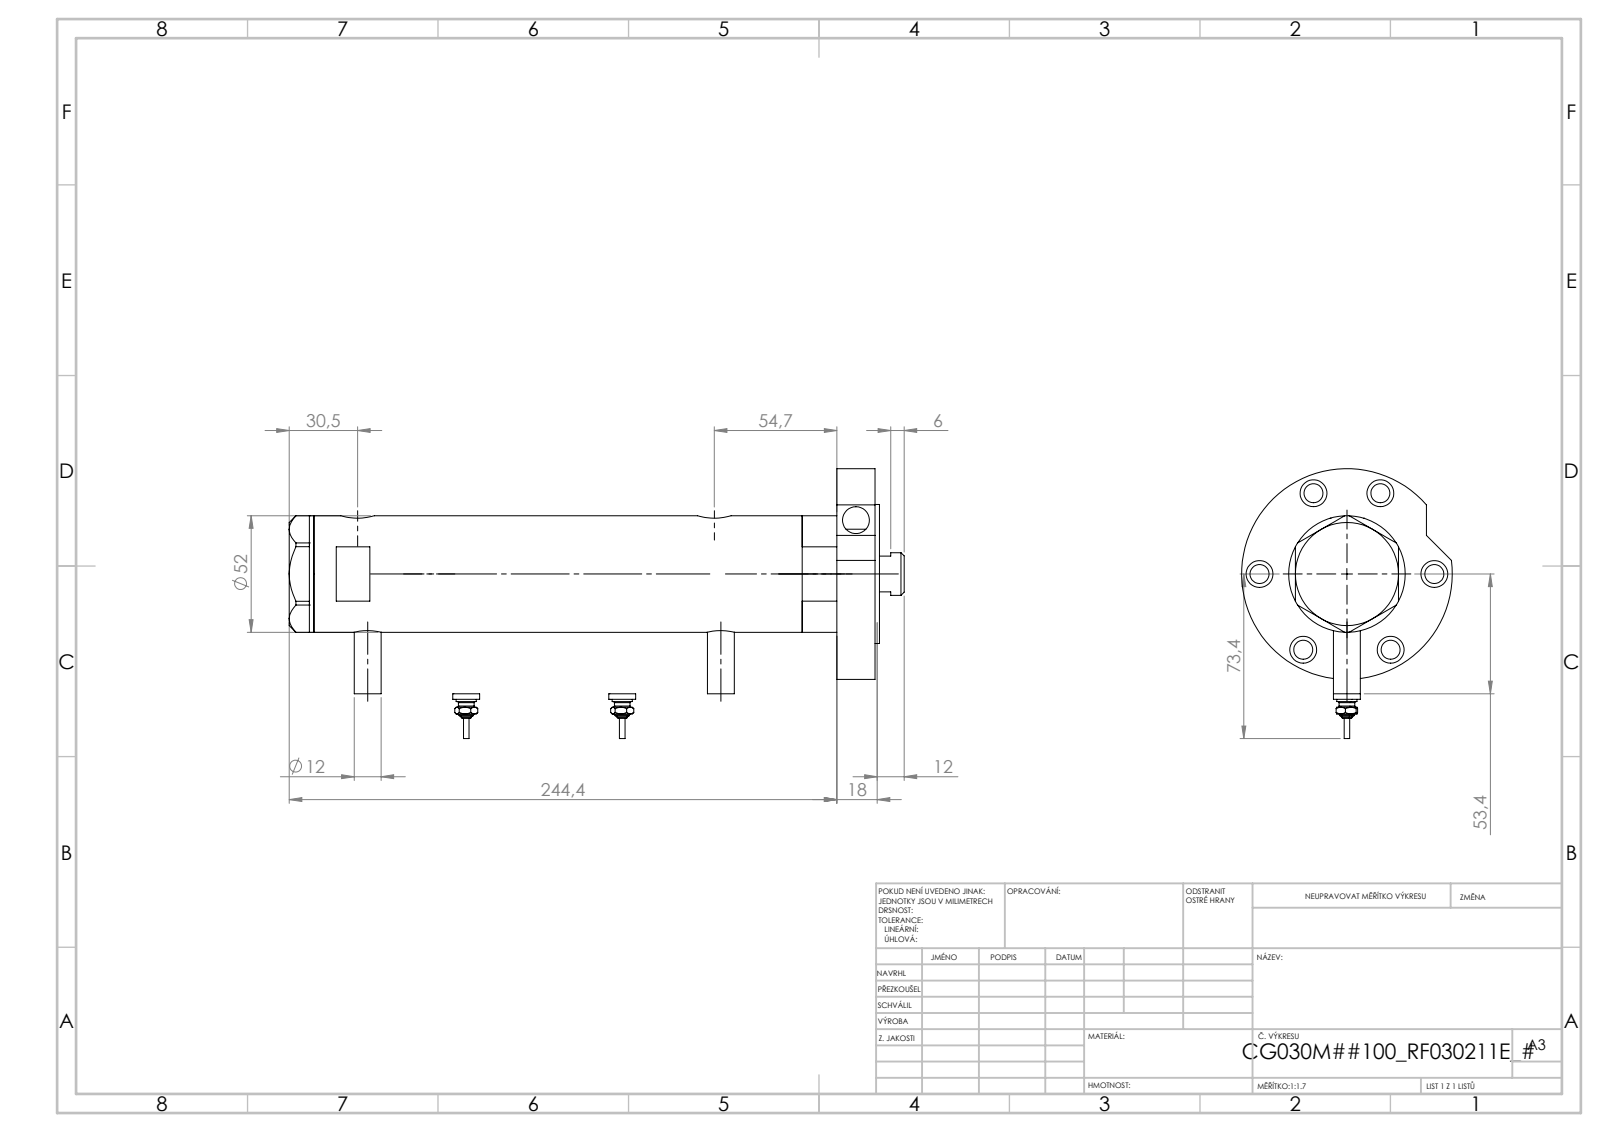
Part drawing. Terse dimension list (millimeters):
name: V270CG_FRONT; V270CG_VC; V270CG_RF211E; V270CG_BACK (+2 more)
written by: SolidWorks 2019 (CONFIG_CONTROL_DESIGN)
unit: mm
bodies: 7 solids, 290 faces (106 planar, 110 cylindrical, 74 other)
size: 249.02 × 105.3 × 94
volume: 525 288 mm³; area: 122 862 mm²
holes: 7× ⌀12, 6× ⌀8.5, 2× ⌀5, 2× ⌀9.73, 2× ⌀12.5, 2× ⌀15, 1× ⌀6.5, 1× ⌀20, 1× ⌀21.5, 1× ⌀30, 1× ⌀33, 1× ⌀40
bosses: 3× ⌀12, 2× ⌀9, 2× ⌀7, 2× ⌀4.34, 2× ⌀2.4, 1× ⌀94, 1× ⌀62, 1× ⌀52
face distances: 17, 205.44, 222.44, 51.9, 2, 224.44, 153.54, 68.9, 70.9, 19
hole spacings: 39, 2.9, 4.5, 43.34, 64.85, 67.55, 69.95, 77.83
